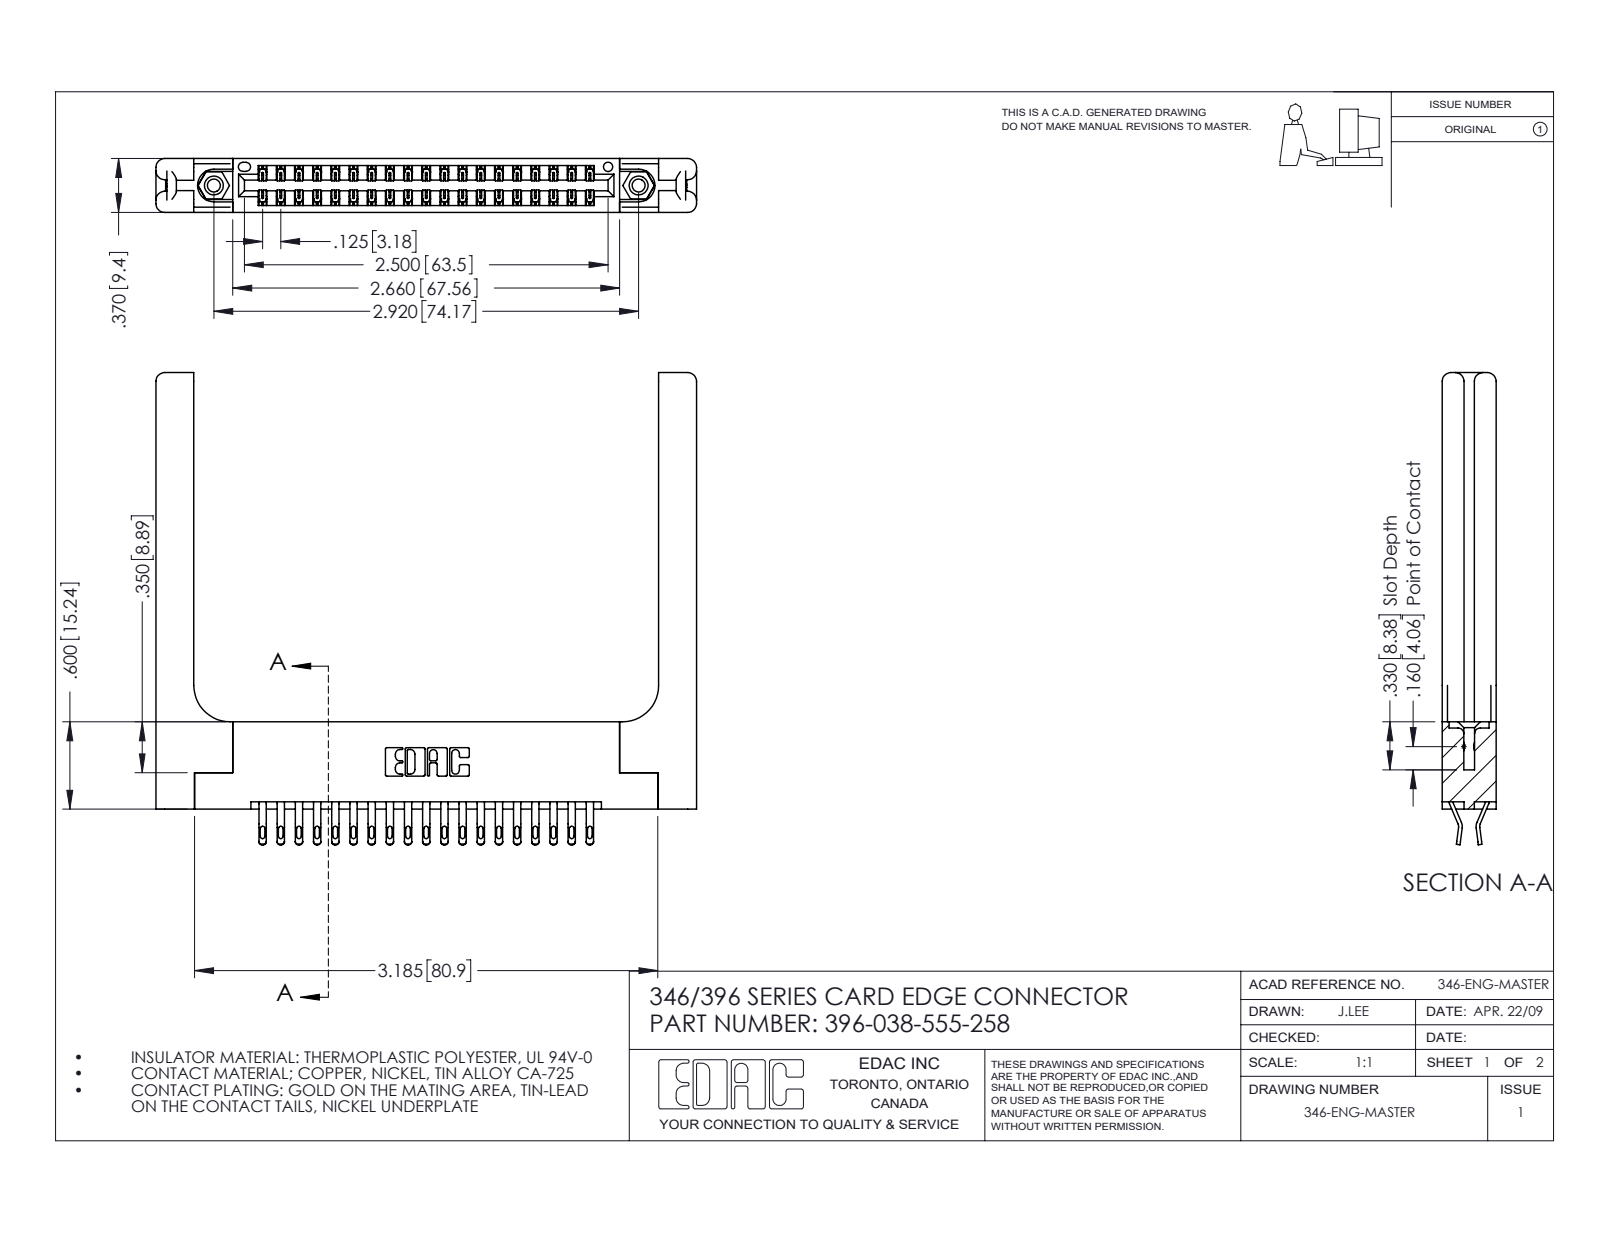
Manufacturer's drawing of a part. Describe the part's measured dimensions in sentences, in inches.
The part is named "345-292-001_555 Tail; 396-038-555-258; 345-250-001_345-250-001-102; 346 Part_Flush Mounting Lugs - 0.156 Dia-TH (+1 more)". Its 3-D file was written by "SolidWorks 2016 (CONFIG_CONTROL_DESIGN)". It is 43 solids with 2582 faces: 1478 planar, 1044 cylindrical and 60 other. Overall it measures 3.716 by 3.245 by 0.37 inches. Its volume is 1.015 cubic inches and its surface area 27.22 square inches. Round holes: 2 of diameter 0.089, 2 of diameter 0.125, 2 of diameter 0.156, 1 of diameter 0.064. Round bosses or shafts: 2 of diameter 0.155. Partial cylindrical surfaces (rounded edges, fillets, slot ends): 76 of radius 0.016, 76 of radius 0.02, 57 of radius 0.006, 22 of radius 0.01, 16 of radius 0.06, 6 of radius 0.007, 6 of radius 0.031, 3 of radius 0.026. The main face-to-face distances are 0.37, 0.072, 0.15, 0.148, 0.048, 0.322, 0.25, 0.025, 0.077, 0.102. The hole center spacings are 0.246, 2.713, 2.92.
